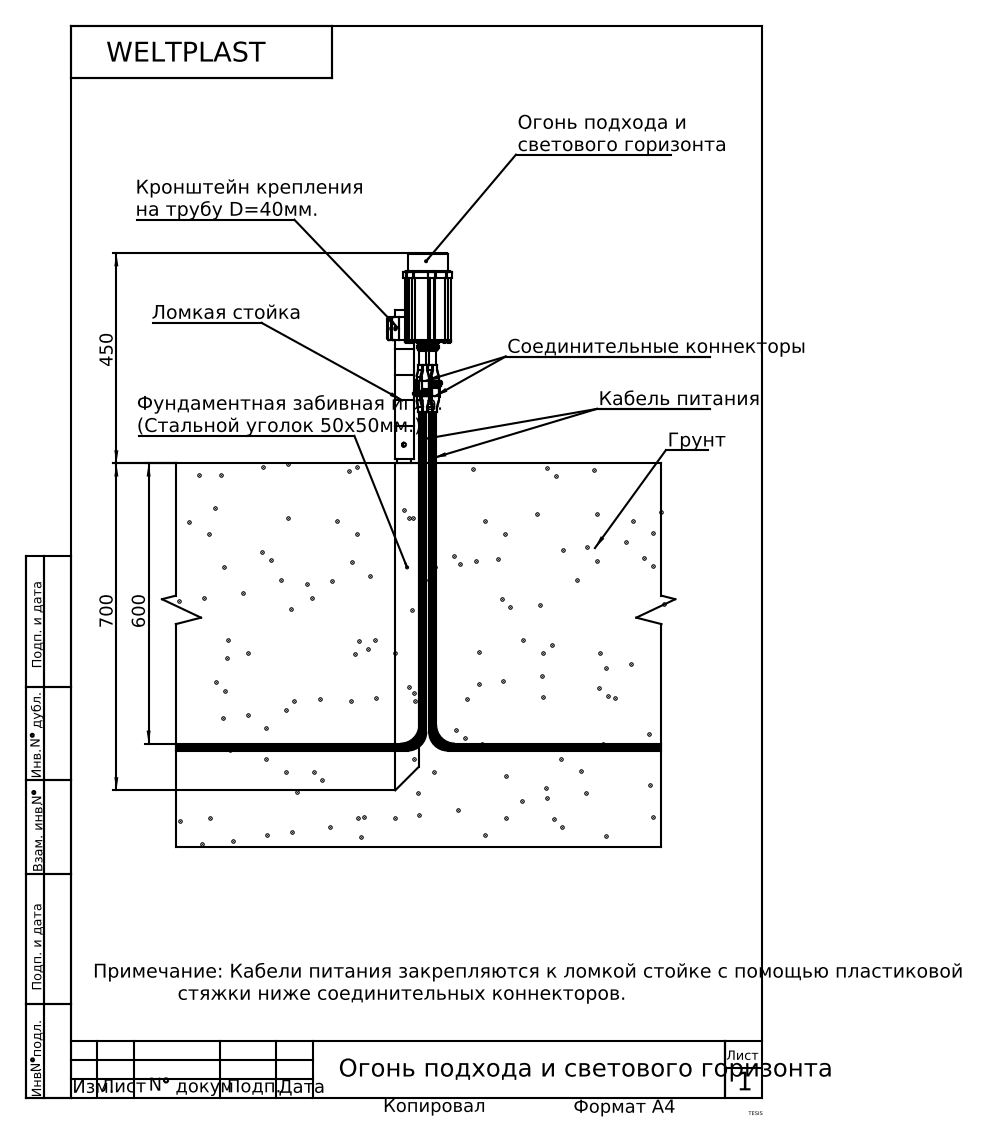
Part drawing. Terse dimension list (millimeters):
name: Фонарь; Скоба_крепления ИГЛА; Втулка; Штырь (+8 more)
written by: SolidWorks 2017 (AUTOMOTIVE_DESIGN)
unit: mm
bodies: 44 solids, 3014 faces (887 planar, 1073 cylindrical, 1054 other)
size: 1150 × 144.43 × 139.12
volume: 912 215 mm³; area: 503 214 mm²
holes: 8× ⌀5.3, 6× ⌀3.6, 6× ⌀4.4, 6× ⌀4.5, 6× ⌀6.3, 3× ⌀2.5, 3× ⌀2.62, 2× ⌀4.2, 2× ⌀6, 2× ⌀12.6, 2× ⌀20.25, 1× ⌀8.3
bosses: 8× ⌀7.6, 8× ⌀4, 2× ⌀21.5, 2× ⌀19.7, 2× ⌀15, 2× ⌀10.5, 2× ⌀6, 1× ⌀85
rounds: 46× R5, 36× R2, 19× R1, 18× R4.5, 14× R1.5, 12× R3, 8× R0.5, 8× R2.5
face distances: 4, 2, 1.5, 3, 5.5, 9.5, 144, 140, 1, 142.5
hole spacings: 47.5, 28, 0.58, 6.37, 34.58, 41.61, 41.7, 43.21
